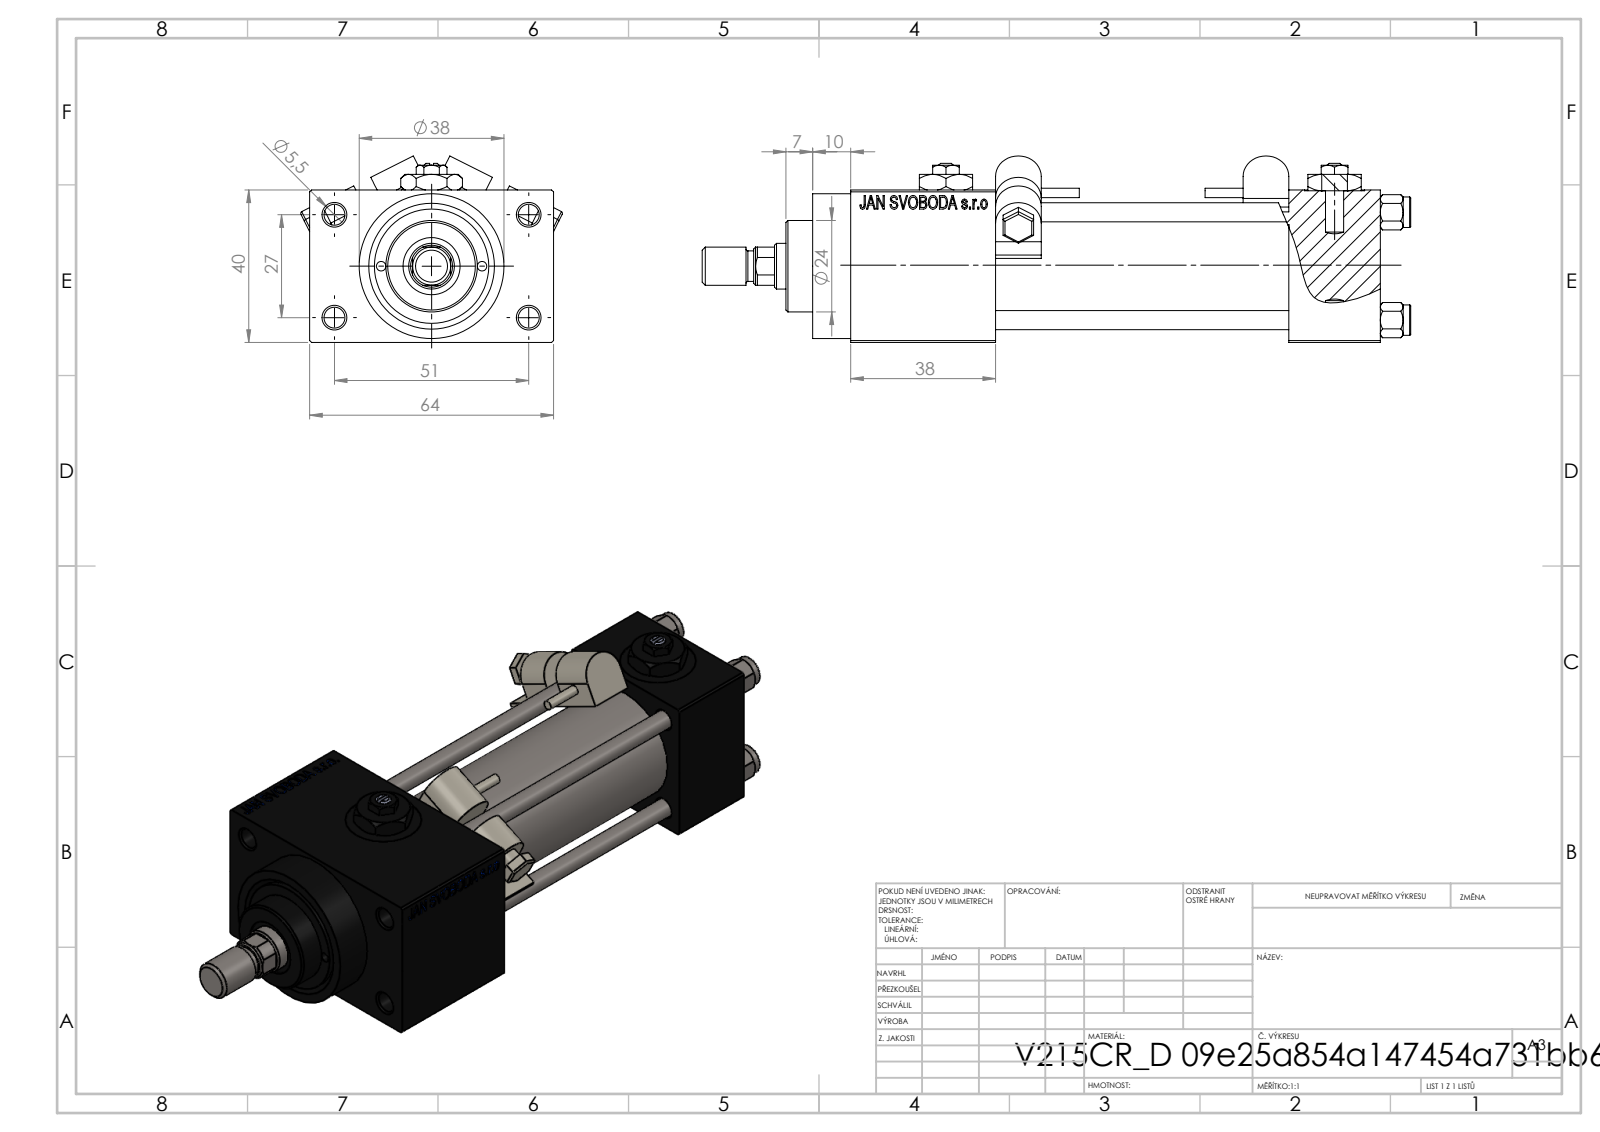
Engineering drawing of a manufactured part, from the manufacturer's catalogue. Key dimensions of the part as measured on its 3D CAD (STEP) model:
Part name (STEP PRODUCT): V215CR_VCP_D; V215_VC_A; MSRF_MSRG1; Zatka_pro_OIL_PORT (+4 more)
STEP written by: SolidWorks 2019 (CONFIG_CONTROL_DESIGN)
Units: millimetres
Bodies: 16 solids, 1288 faces (584 planar, 136 cylindrical, 568 other)
Overall size (bounding box): 186 × 68.71 × 48.93
Volume: 195 653 mm³ · Surface area: 76 369 mm²
Round holes (diameter × count): ⌀5 ×4, ⌀5.5 ×4, ⌀20 ×3, ⌀2.5 ×2, ⌀7 ×2, ⌀13.16 ×2, ⌀6.5 ×1, ⌀12 ×1, ⌀15 ×1, ⌀25 ×1, ⌀30 ×1
Round bosses / shafts (diameter × count): ⌀8 ×5, ⌀5 ×2, ⌀2.5 ×2, ⌀38 ×1, ⌀31 ×1, ⌀24 ×1, ⌀10 ×1
Partial cylindrical surfaces — rounded edges, fillets, slot ends (radius × count): R0.5 ×12, R6 ×4, R5.5 ×1
Main face-to-face distances: 40, 12, 77, 52, 24, 101, 38, 64, 115, 139
Hole centre spacings: 11.37, 14.18, 18.23, 20.01, 28.3, 28.85, 29.89, 30.84
